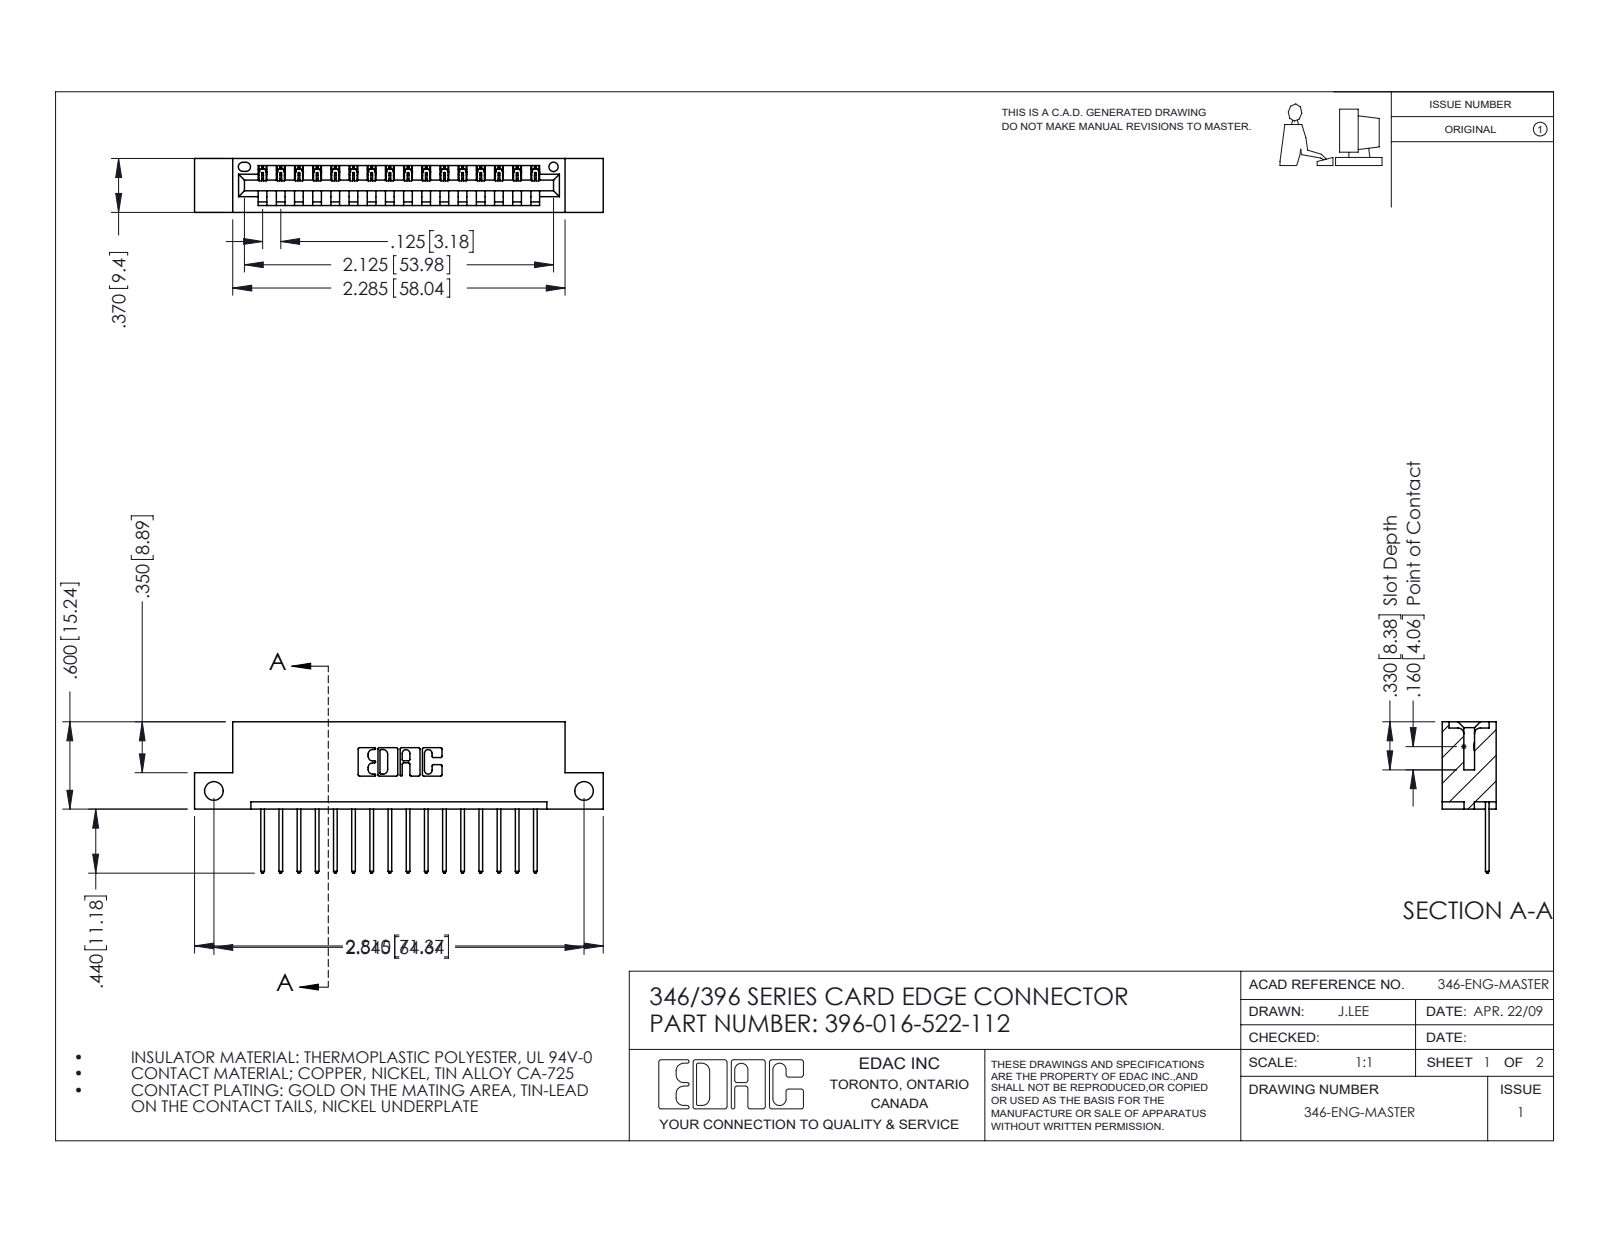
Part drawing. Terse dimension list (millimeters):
name: 396-016-522-112; 345-292-001_345-293-122; 346 Part_Flush Mounting Lugs - Side Mount
written by: SolidWorks 2016 (CONFIG_CONTROL_DESIGN)
unit: mm
bodies: 17 solids, 1050 faces (716 planar, 334 cylindrical, 0 other)
size: 71.4 × 26.4 × 9.4
volume: 6 570 mm³; area: 7 839 mm²
holes: 2× ⌀3.3, 1× ⌀1.6
rounds: 32× R0.2, 32× R0.3, 22× R0.3, 6× R0.2, 6× R0.8, 3× R0.7, 2× R0.8, 2× R1
face distances: 1.2, 8.2, 6.4, 9.4, 1.8, 7.6, 0.6, 3.8, 5.6, 2.5
hole spacings: 64.6
